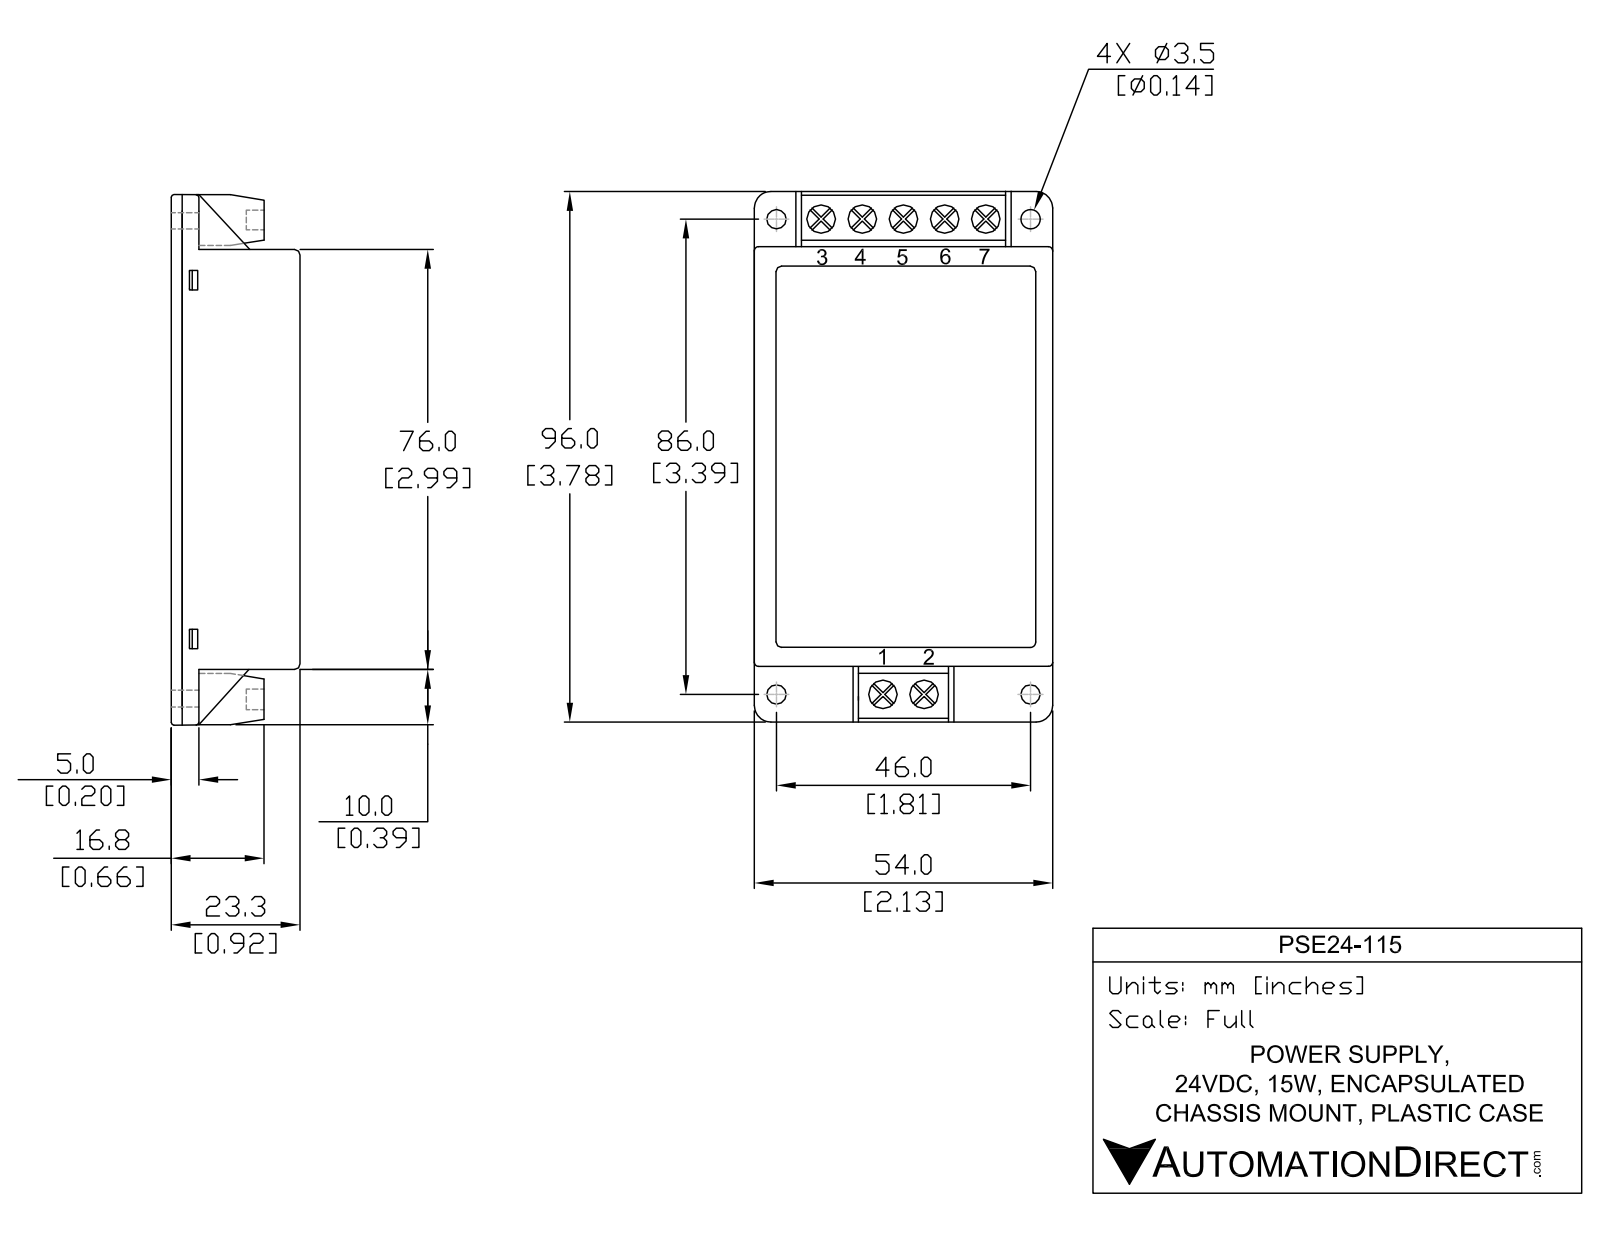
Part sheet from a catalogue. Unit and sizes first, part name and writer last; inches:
Units: inches
Overall size (bounding box): 3.78 × 2.13 × 0.92
Round holes (diameter × count): ⌀0.2 ×7, ⌀0.14 ×4
Partial cylindrical surfaces — rounded edges, fillets, slot ends (radius × count): R0.03 ×20, R0.125 ×4
Main face-to-face distances: 0.078, 0.08, 0.84, 0.918, 0.838, 2.13, 2.99, 0.92, 0.842, 0.015
Hole centre spacings: 0.26, 0.52, 0.26, 0.775, 1.035, 1.81, 3.362, 3.363
Volume: 6.464 in³ · Surface area: 45.54 in²
Bodies: 2 solids, 369 faces (246 planar, 62 cylindrical, 61 other)
Part name (STEP PRODUCT): PSE24-115
STEP written by: SolidWorks 2011 (CONFIG_CONTROL_DESIGN)
